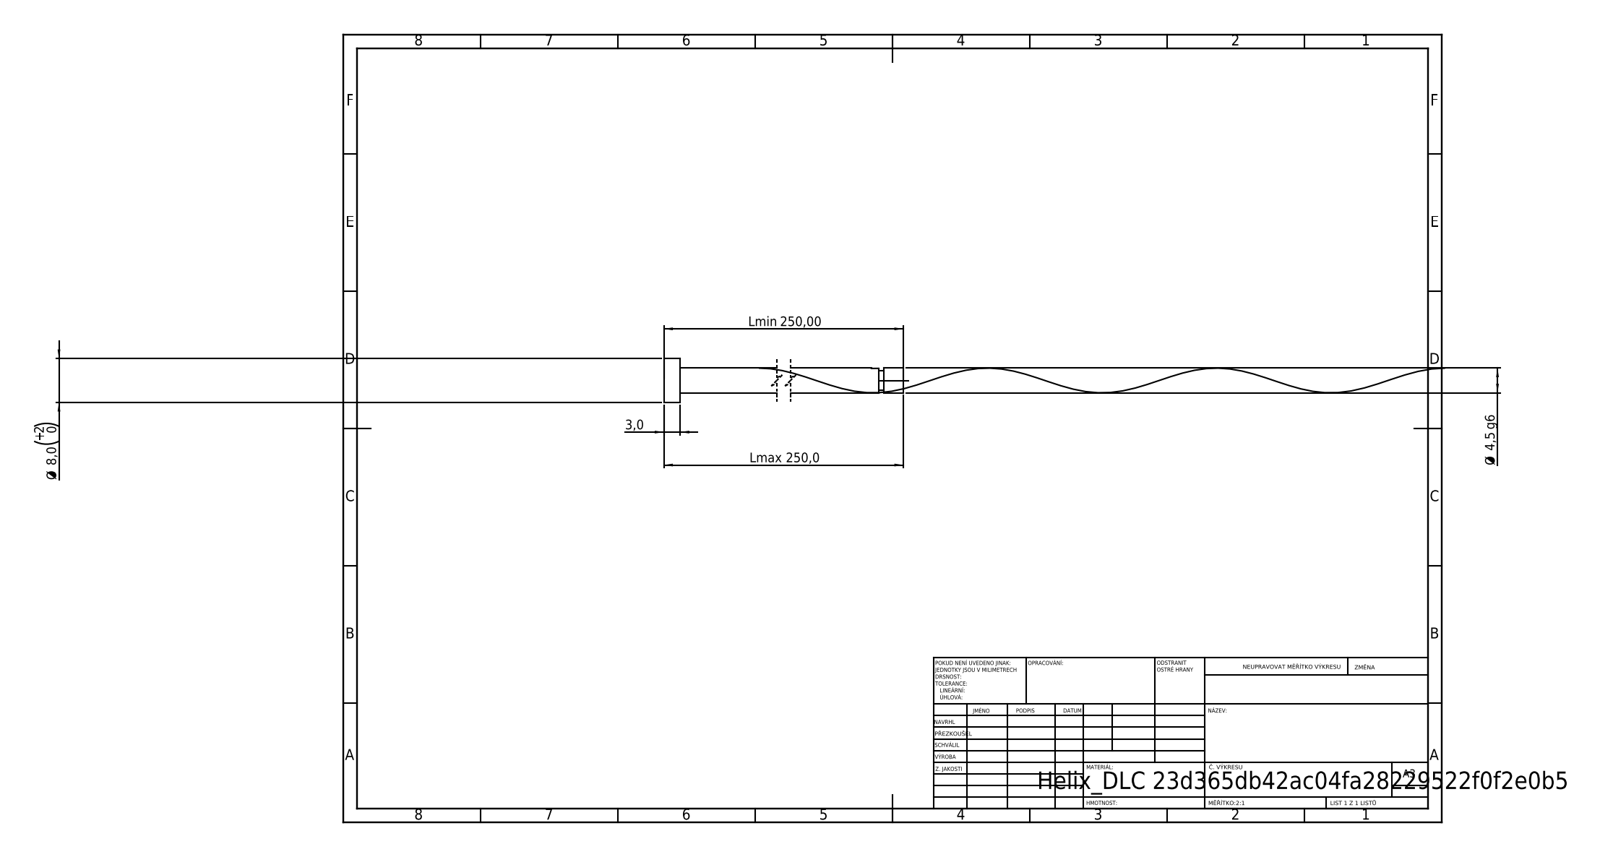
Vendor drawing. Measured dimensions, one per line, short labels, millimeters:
written by: SolidWorks 2019 (CONFIG_CONTROL_DESIGN)
unit: mm
bodies: 1 solid, 16 faces (6 planar, 9 cylindrical, 1 other)
size: 250 × 8 × 8
volume: 4 920 mm³; area: 4 913 mm²
bosses: 1× ⌀8, 1× ⌀4.5, 1× ⌀3.6
face distances: 3, 250, 247, 246.38, 243.38, 3.62, 245.48, 242.48, 0.9, 4.52
